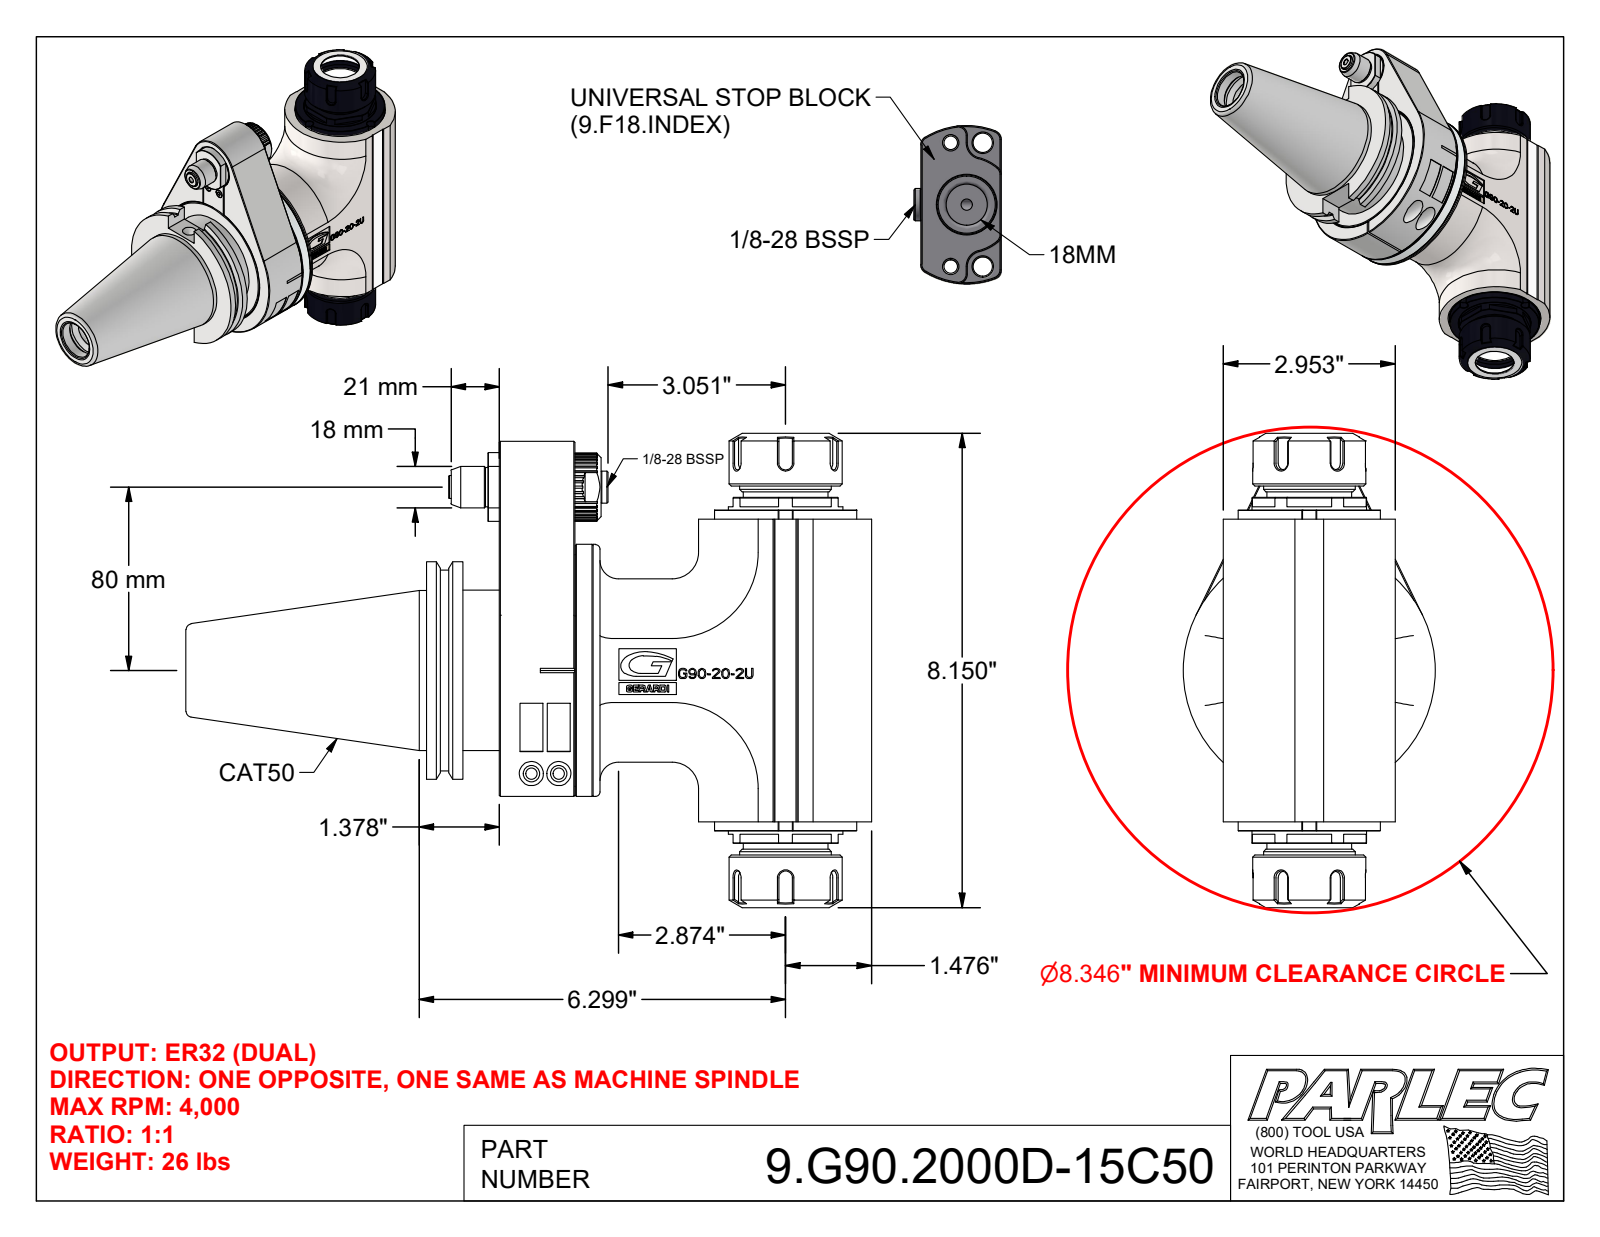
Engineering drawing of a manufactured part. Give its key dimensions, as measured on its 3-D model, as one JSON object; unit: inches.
{"part_name": "9.G90.2000D-15C50; 9_GA2_458_1 (Classic, Type 2, Cat50, 80mm); 9_G90_202U0", "step_written_by": "Autodesk Inventor 2022 (AUTOMOTIVE_DESIGN)", "units": "inches", "bodies": {"solids": 5, "faces": 1561, "planar": 912, "cylindrical": 288, "other": 361}, "overall_size": [11.783, 8.15, 4.331], "volume_in3": 96.69, "surface_area_in2": 421, "round_holes": [[0.197, 10], [0.118, 8], [0.13, 5], [0.335, 3], [0.157, 2], [0.165, 2], [0.236, 2], [0.276, 2], [0.413, 2], [0.709, 2], [0.984, 2], [0.433, 1]], "round_bosses_or_shafts": [[0.394, 2], [4.331, 1], [4.016, 1], [3.875, 1], [3.593, 1], [3.524, 1], [3.15, 1], [2.756, 1]], "partial_cylinders_radius": [[0.059, 16], [0.118, 12], [0.098, 3], [0.085, 2], [0.315, 2], [1.575, 2], [0.079, 1], [0.115, 1]], "face_to_face_distances": [1.299, 0.197, 0.315, 0.626, 0.984, 1.102, 1.673, 2.953, 0.118, 0.02], "hole_center_spacings": [1.87, 0.389, 0.505, 0.713, 0.855, 1.1, 1.338, 0.283]}
